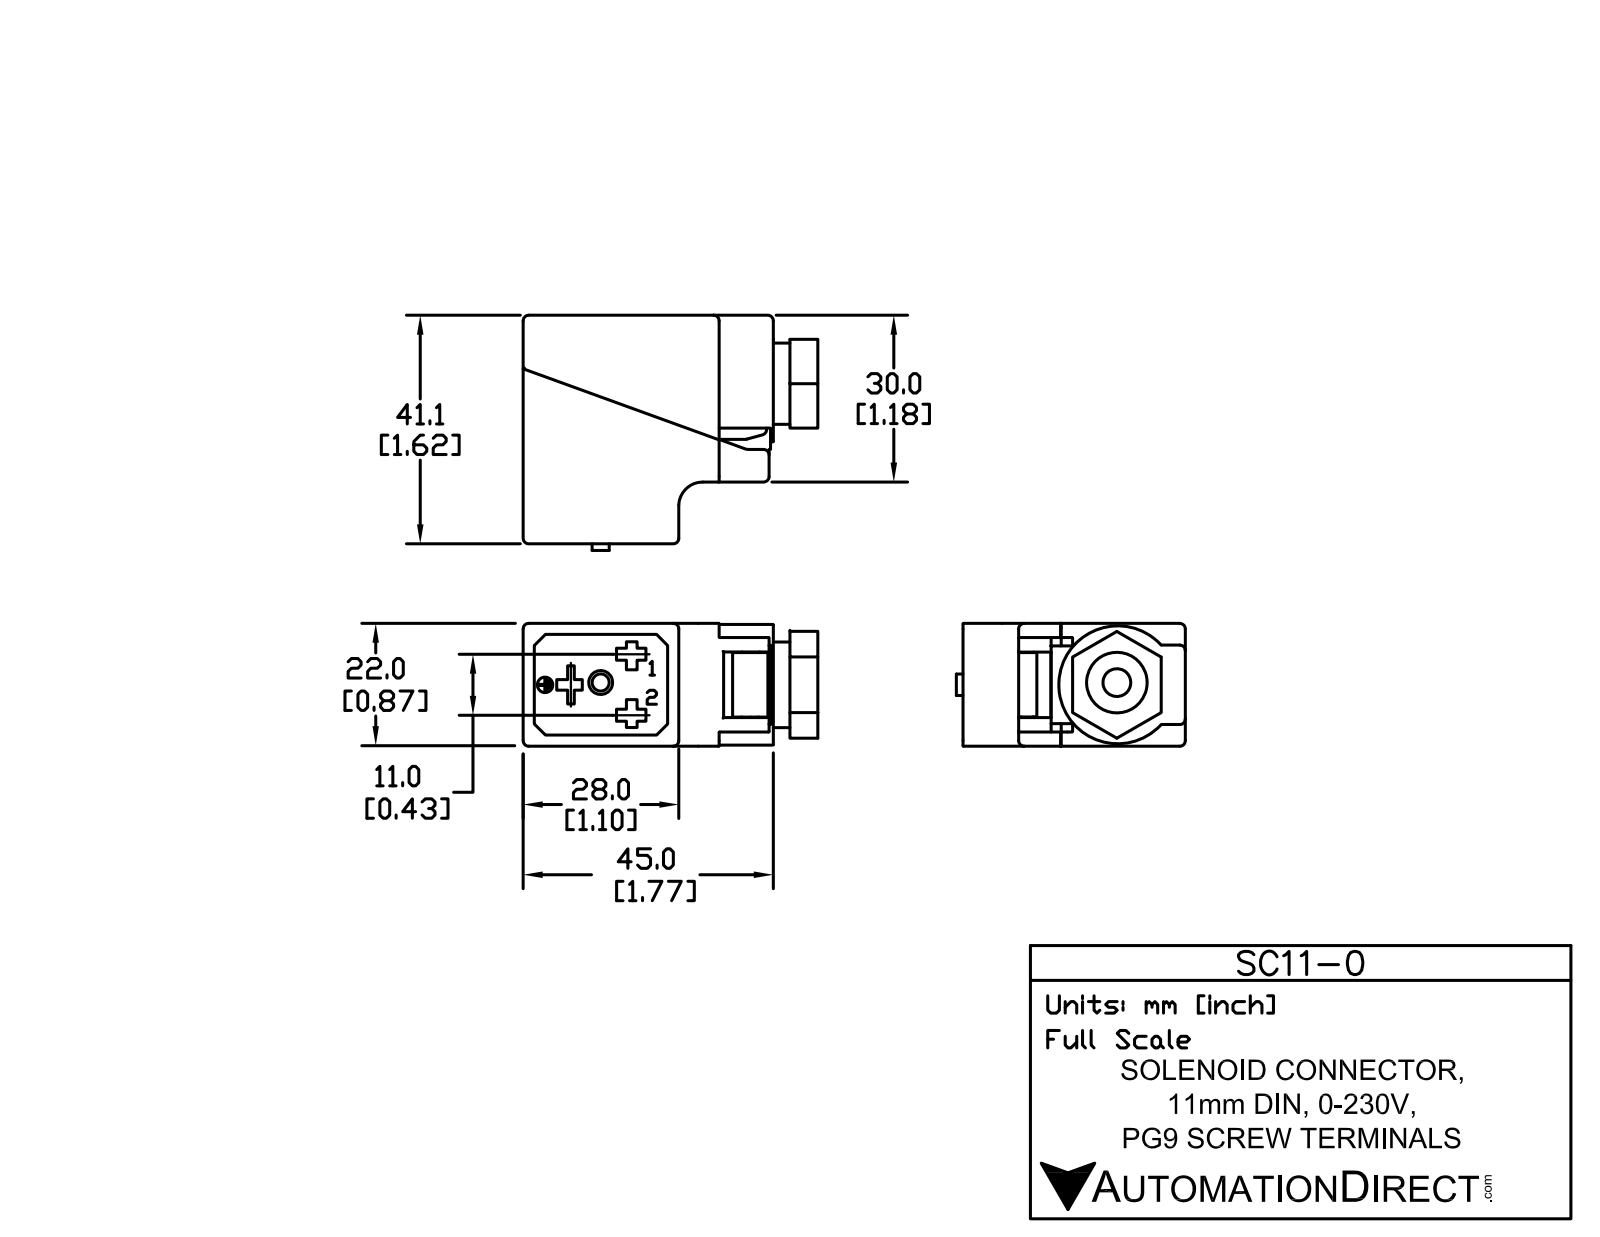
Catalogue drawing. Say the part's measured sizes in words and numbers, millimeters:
The part is named "SC11-0". Its 3-D file was written by "SolidWorks 2011 (AUTOMOTIVE_DESIGN)". It is 8 solids with 502 faces: 384 planar, 71 cylindrical and 47 other. Overall it measures 53.55 by 46 by 21.5 millimeters. Its volume is 23 530 cubic millimeters and its surface area 18 822 square millimeters. Round holes: 1 of diameter 2.5, 1 of diameter 3, 1 of diameter 3.5, 1 of diameter 3.75, 1 of diameter 5.5, 1 of diameter 5.75, 1 of diameter 7, 1 of diameter 9.4, 1 of diameter 10, 1 of diameter 10.1, 1 of diameter 11, 1 of diameter 14. Round bosses or shafts: 2 of diameter 1.5, 1 of diameter 15, 1 of diameter 13.5, 1 of diameter 13.4, 1 of diameter 11.7, 1 of diameter 5.9, 1 of diameter 3, 1 of diameter 2.9. Partial cylindrical surfaces (rounded edges, fillets, slot ends): 12 of radius 1, 12 of radius 2, 2 of radius 0.36, 2 of radius 1.5, 1 of radius 0.5, 1 of radius 1.36, 1 of radius 1.43, 1 of radius 1.5. The main face-to-face distances are 2.35, 16.8, 2, 2.3, 19.1, 19.15, 21.45, 21.15, 0.35, 21.1. The hole center spacings are 7.36, 7.57.
